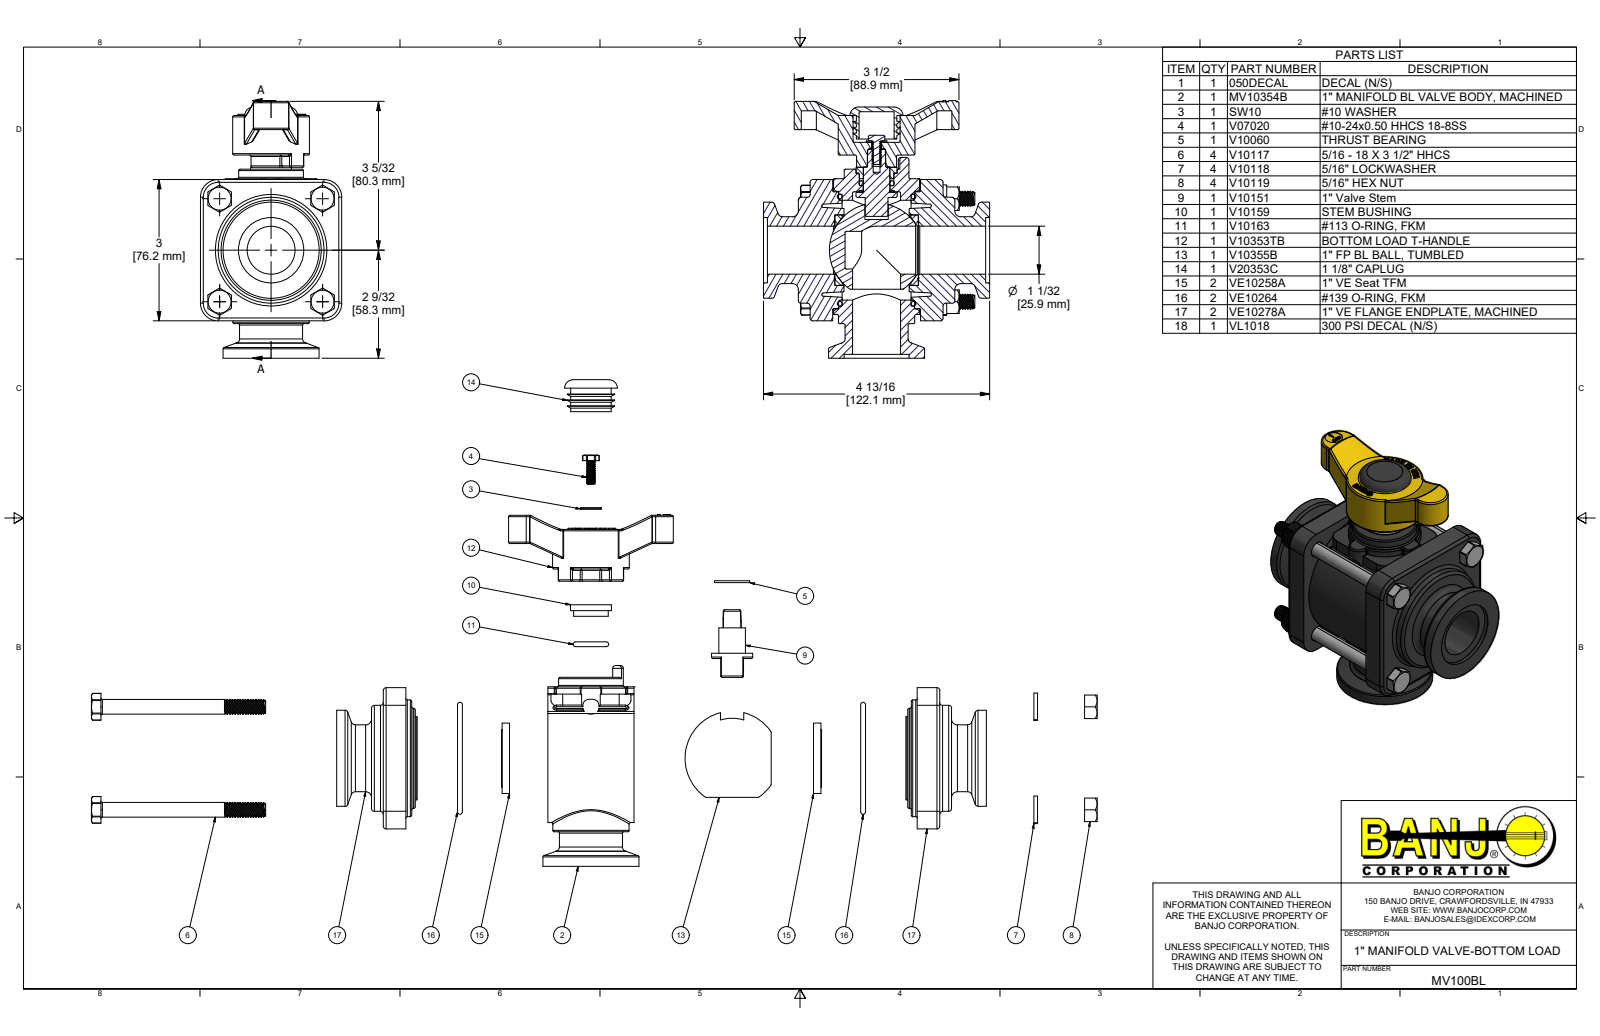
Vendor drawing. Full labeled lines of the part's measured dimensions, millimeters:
Part name (STEP PRODUCT): MV100BL; MV10354B; MV10354BX; VE10278A (+8 more)
STEP written by: Autodesk Inventor 2019 (AUTOMOTIVE_DESIGN)
Units: millimetres
Bodies: 28 solids, 2172 faces (698 planar, 684 cylindrical, 790 other)
Overall size (bounding box): 138.9 × 122.1 × 76.2
Volume: 393 100 mm³ · Surface area: 140 500 mm²
Round holes (diameter × count): ⌀6.4 ×4, ⌀8.2 ×4, ⌀8.9 ×4, ⌀25.9 ×2, ⌀2.3 ×1, ⌀3.3 ×1, ⌀3.7 ×1, ⌀5.2 ×1, ⌀5.3 ×1, ⌀9.5 ×1, ⌀14.2 ×1, ⌀14.3 ×1
Round bosses / shafts (diameter × count): ⌀6.8 ×60, ⌀14.8 ×4, ⌀8 ×4, ⌀51.8 ×2, ⌀69.3 ×1, ⌀63 ×1, ⌀57.2 ×1, ⌀53.9 ×1
Partial cylindrical surfaces — rounded edges, fillets, slot ends (radius × count): R0.8 ×74, R0.8 ×12, R1.5 ×10, R9.5 ×10, R1.6 ×8, R3.4 ×8, R0.6 ×6, R5.3 ×4
Main face-to-face distances: 12.2, 59.6, 71.8, 76.2, 25.1, 37.3, 84.7, 96.9, 47.4, 2
Hole centre spacings: 39.3, 55.6, 78.6, 16.8, 38.9, 46.5
